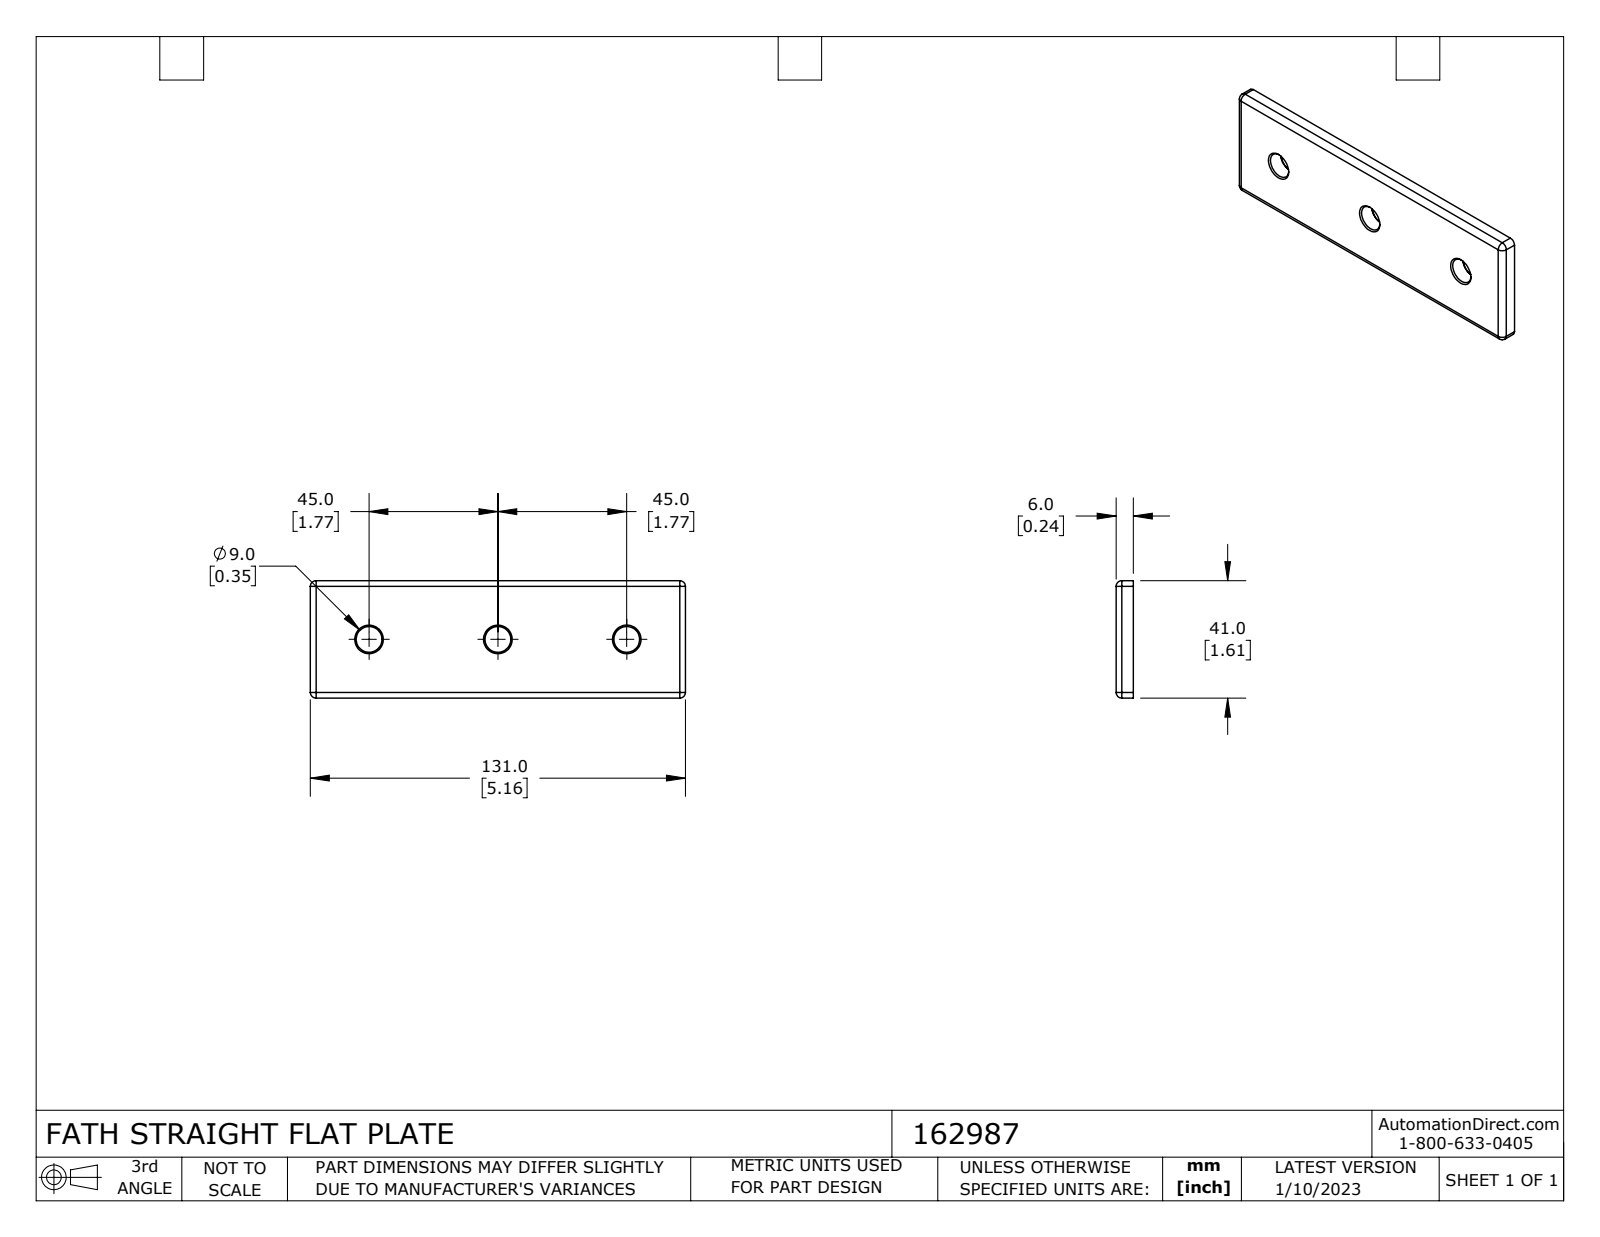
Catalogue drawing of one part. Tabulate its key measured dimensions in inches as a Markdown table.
| quantity | value |
| --- | --- |
| part name | 162987 |
| STEP written by | SolidWorks 2021 (CONFIG_CONTROL_DESIGN) |
| units | inches |
| bodies | 1 solid, 36 faces (6 planar, 14 cylindrical, 16 other) |
| overall size | 5.157 × 1.614 × 0.236 |
| volume | 1.876 in³ |
| surface area | 19.47 in² |
| round holes (diameter × count) | 0.354 × 3 |
| partial cylindrical surfaces (radius × count) | 0.079 × 8 |
| main face-to-face distances | 0.236, 1.614, 5.157 |
| hole center spacings | 1.772, 3.543 |
